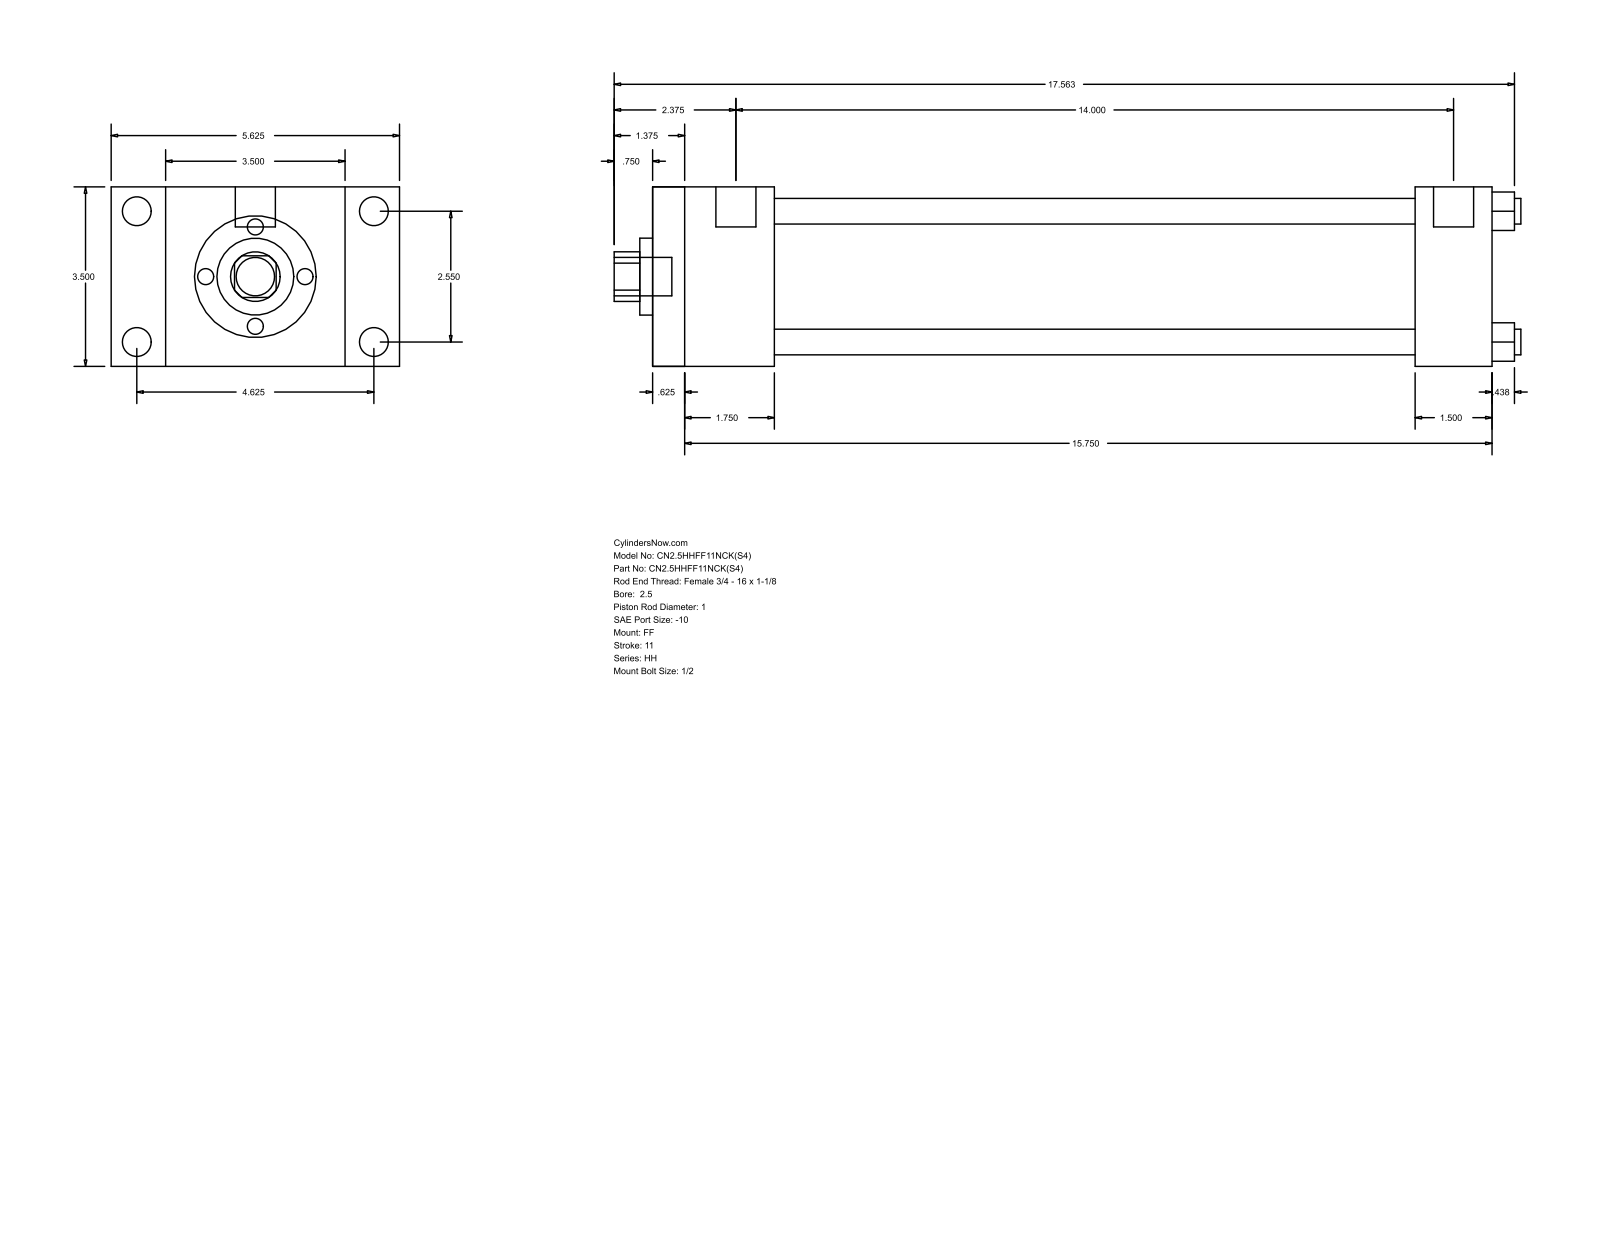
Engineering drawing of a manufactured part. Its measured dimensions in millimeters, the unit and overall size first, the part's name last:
Units: millimetres
Overall size (bounding box): 449.26 × 142.88 × 88.9
Round holes (diameter × count): ⌀12.7 ×4, ⌀25.4 ×1, ⌀38.1 ×1, ⌀73.03 ×1
Round bosses / shafts (diameter × count): ⌀14.3 ×4, ⌀5.56 ×4, ⌀19.84 ×2, ⌀19.05 ×1
Partial cylindrical surfaces — rounded edges, fillets, slot ends (radius × count): R12.29 ×1
Main face-to-face distances: 88.9, 415.93, 15.87, 400.06, 60.33, 44.46, 355.6, 377.83, 361.96, 317.5
Hole centre spacings: 45.79, 64.76, 91.58
Bodies: 0 solids, 92 faces (64 planar, 28 cylindrical, 0 other)
Part name (STEP PRODUCT): HH_FF__0250_1
STEP written by: GSSL Pune (CONFIG_CONTROL_DESIGN)
